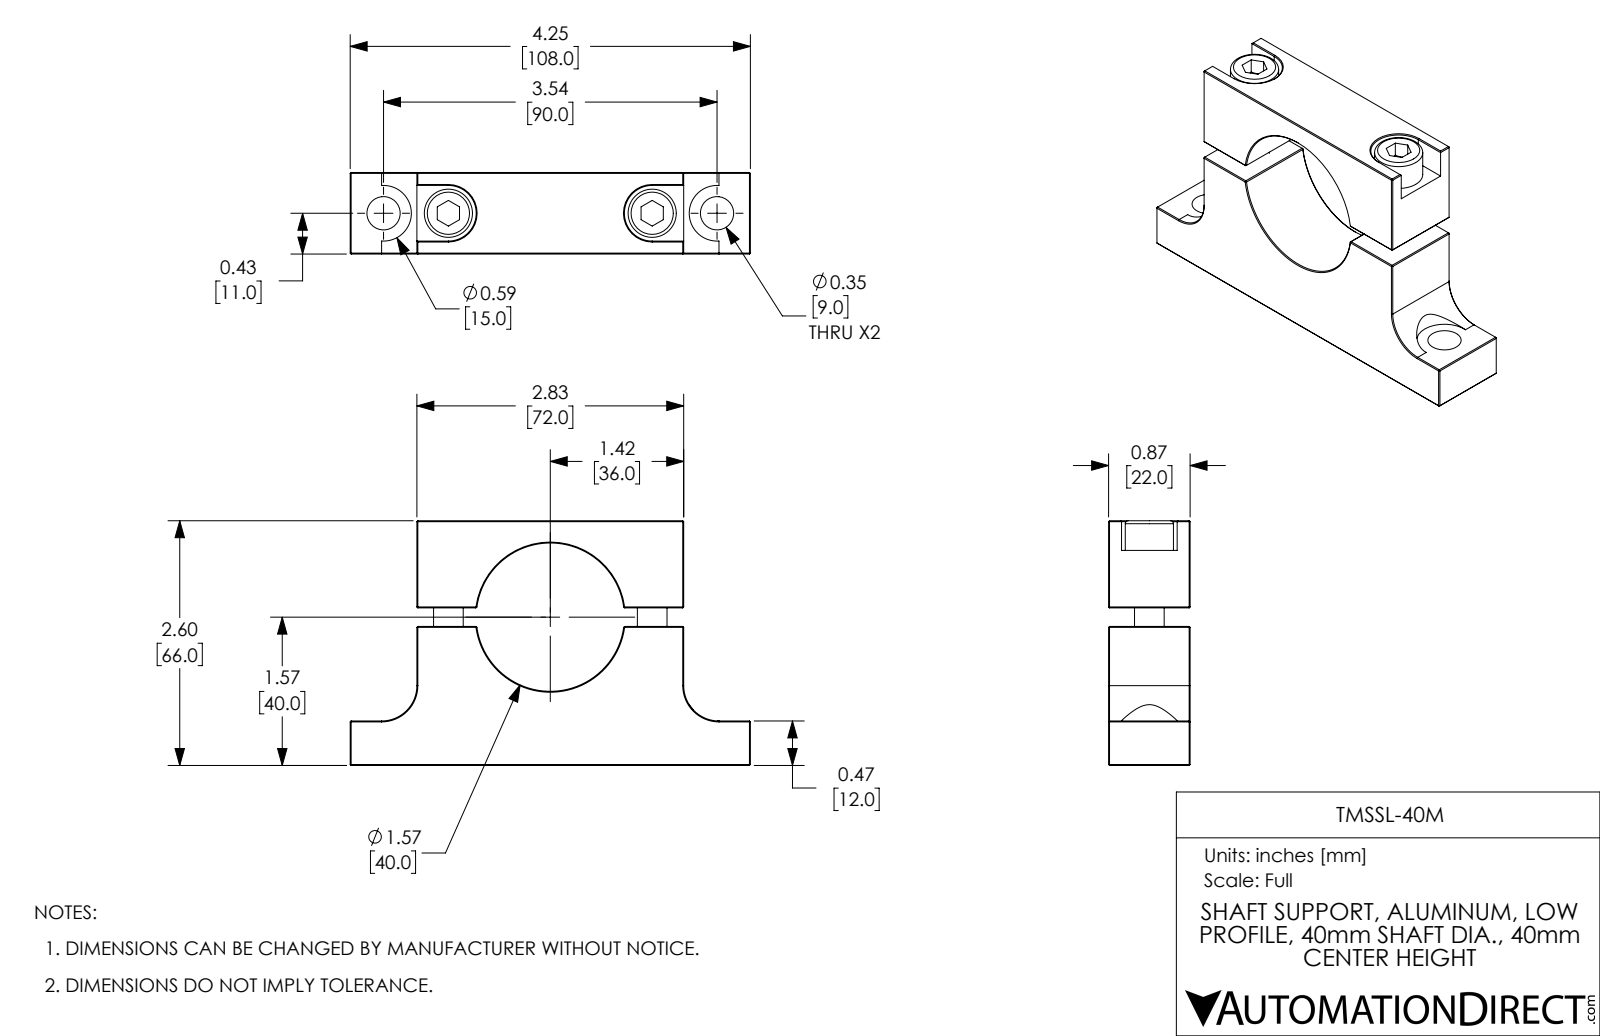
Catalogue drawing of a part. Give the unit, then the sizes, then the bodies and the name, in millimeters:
Units: millimetres
Overall size (bounding box): 108 × 66 × 22
Round holes (diameter × count): ⌀9 ×4, ⌀6.7 ×2, ⌀2.4 ×1, ⌀40 ×1
Round bosses / shafts (diameter × count): ⌀13 ×2, ⌀8 ×2
Partial cylindrical surfaces — rounded edges, fillets, slot ends (radius × count): R7.5 ×4, R9.5 ×2
Main face-to-face distances: 22, 66, 72, 37.5, 28.5, 23.5, 42.5, 5, 18, 90
Hole centre spacings: 17.5, 27.5, 45, 72.5, 55, 90
Volume: 78 740 mm³ · Surface area: 24 420 mm²
Bodies: 4 solids, 178 faces (118 planar, 32 cylindrical, 28 other)
Part name (STEP PRODUCT): TMSSL-40M
STEP written by: SolidWorks 2017 (AUTOMOTIVE_DESIGN)
